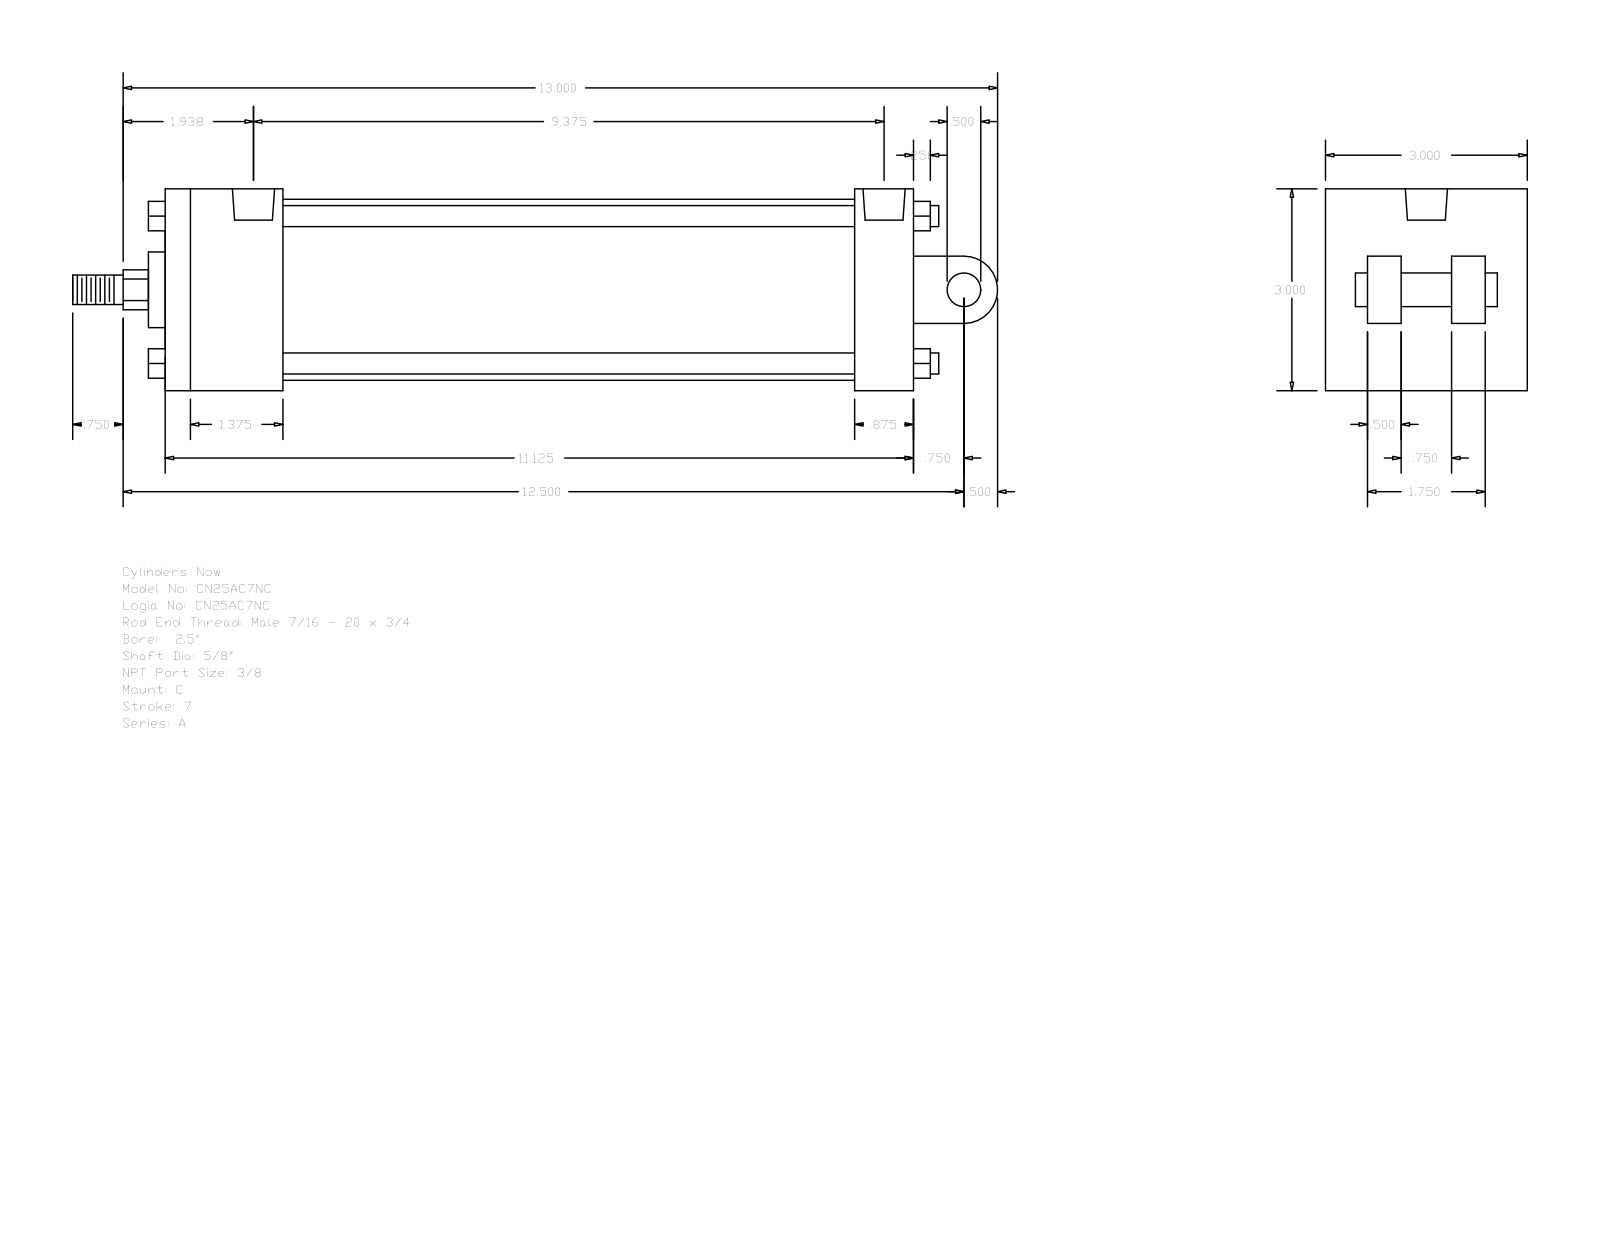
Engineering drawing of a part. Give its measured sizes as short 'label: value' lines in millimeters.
name: A_C__0250_0.625
written by: GSSL Pune (CONFIG_CONTROL_DESIGN)
unit: mm
bodies: 0 solids, 135 faces (102 planar, 33 cylindrical, 0 other)
size: 349.25 × 76.2 × 76.2
holes: 4× ⌀5.56, 2× ⌀15.93
bosses: 4× ⌀7.94, 1× ⌀68.33, 1× ⌀28.57, 1× ⌀15.88, 1× ⌀12.7, 1× ⌀11.11
rounds: 1× R7.54, 1× R12.7
face distances: 76.2, 282.57, 44.45, 260.35, 215.9, 238.12, 22.22, 50.8, 12.7, 25.4
hole spacings: 2.38, 240.51, 242.89, 238.13
